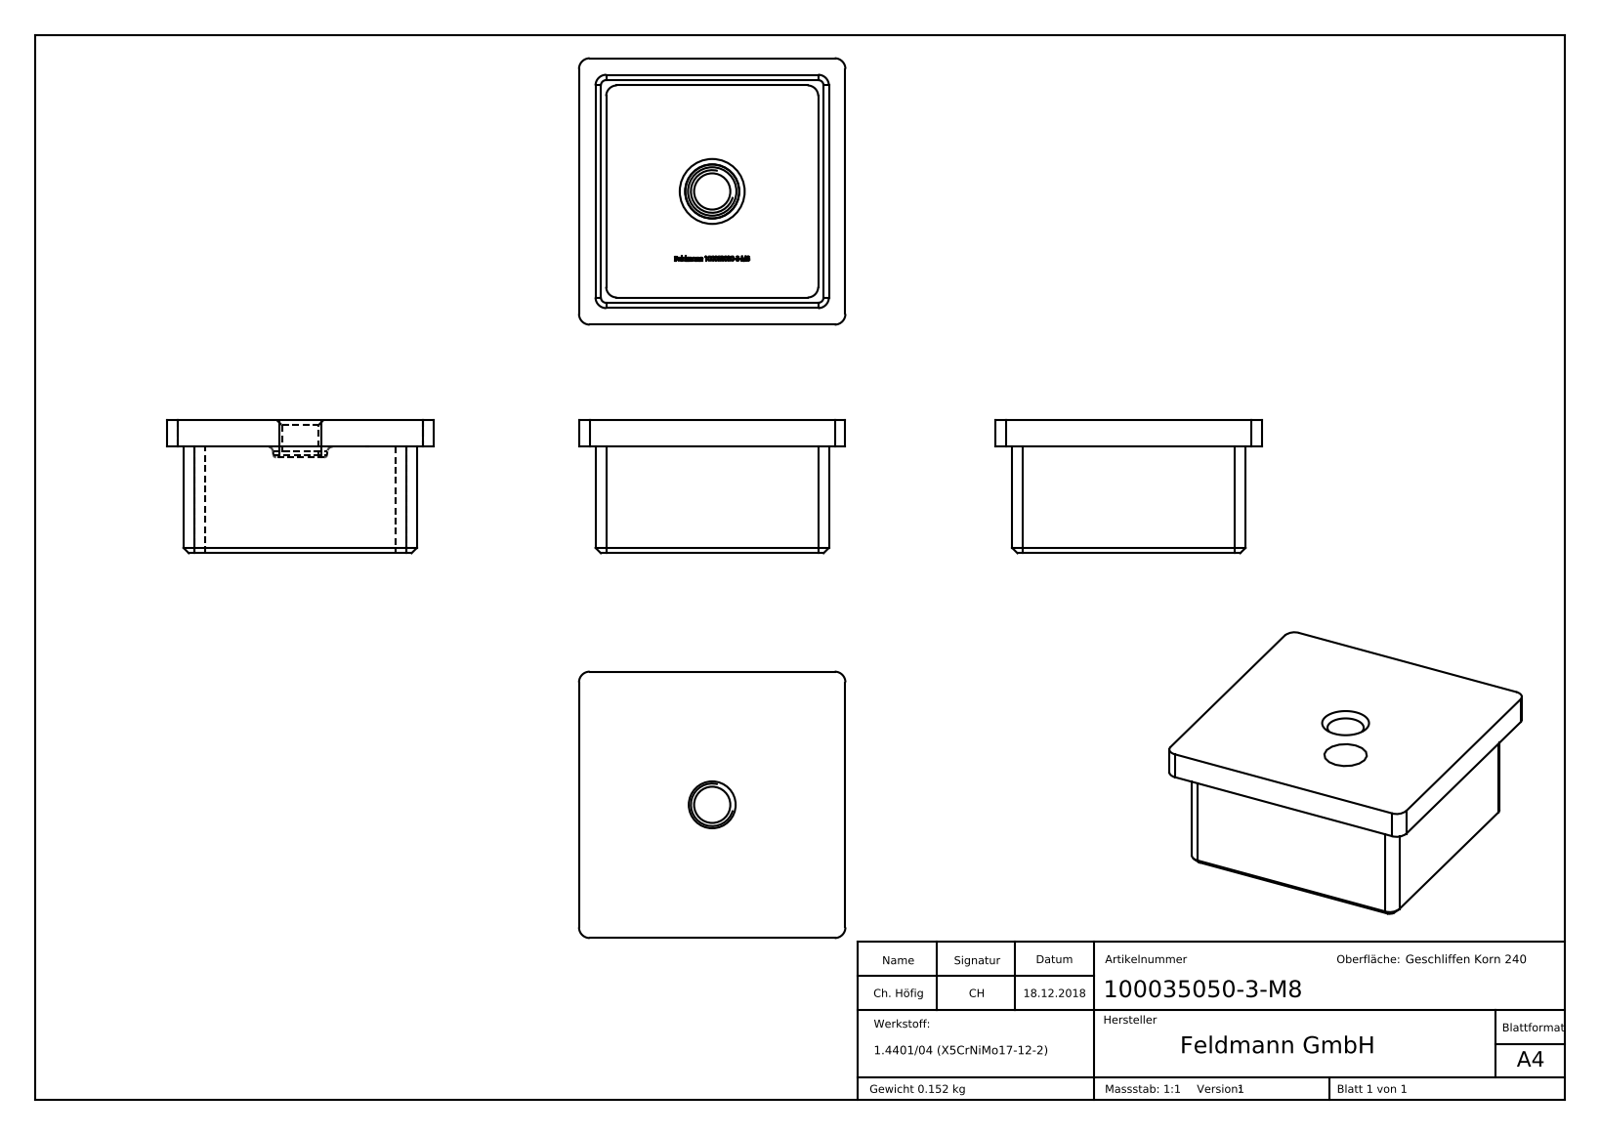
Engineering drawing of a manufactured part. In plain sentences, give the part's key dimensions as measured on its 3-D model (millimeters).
The part is named "100035050-3-M8". Its 3-D file was written by "SolidWorks 2015 (CONFIG_CONTROL_DESIGN)". It is 1 solid with 332 faces: 152 planar, 14 cylindrical and 166 other. Overall it measures 50 by 50 by 25 millimeters. Its volume is 18 987 cubic millimeters and its surface area 12 540 square millimeters. Round holes: 1 of diameter 6.8. Partial cylindrical surfaces (rounded edges, fillets, slot ends): 12 of radius 2. The main face-to-face distances are 2, 41.8, 5, 43.8, 39.8, 3.1, 5.1, 44.9, 46.9, 50.
